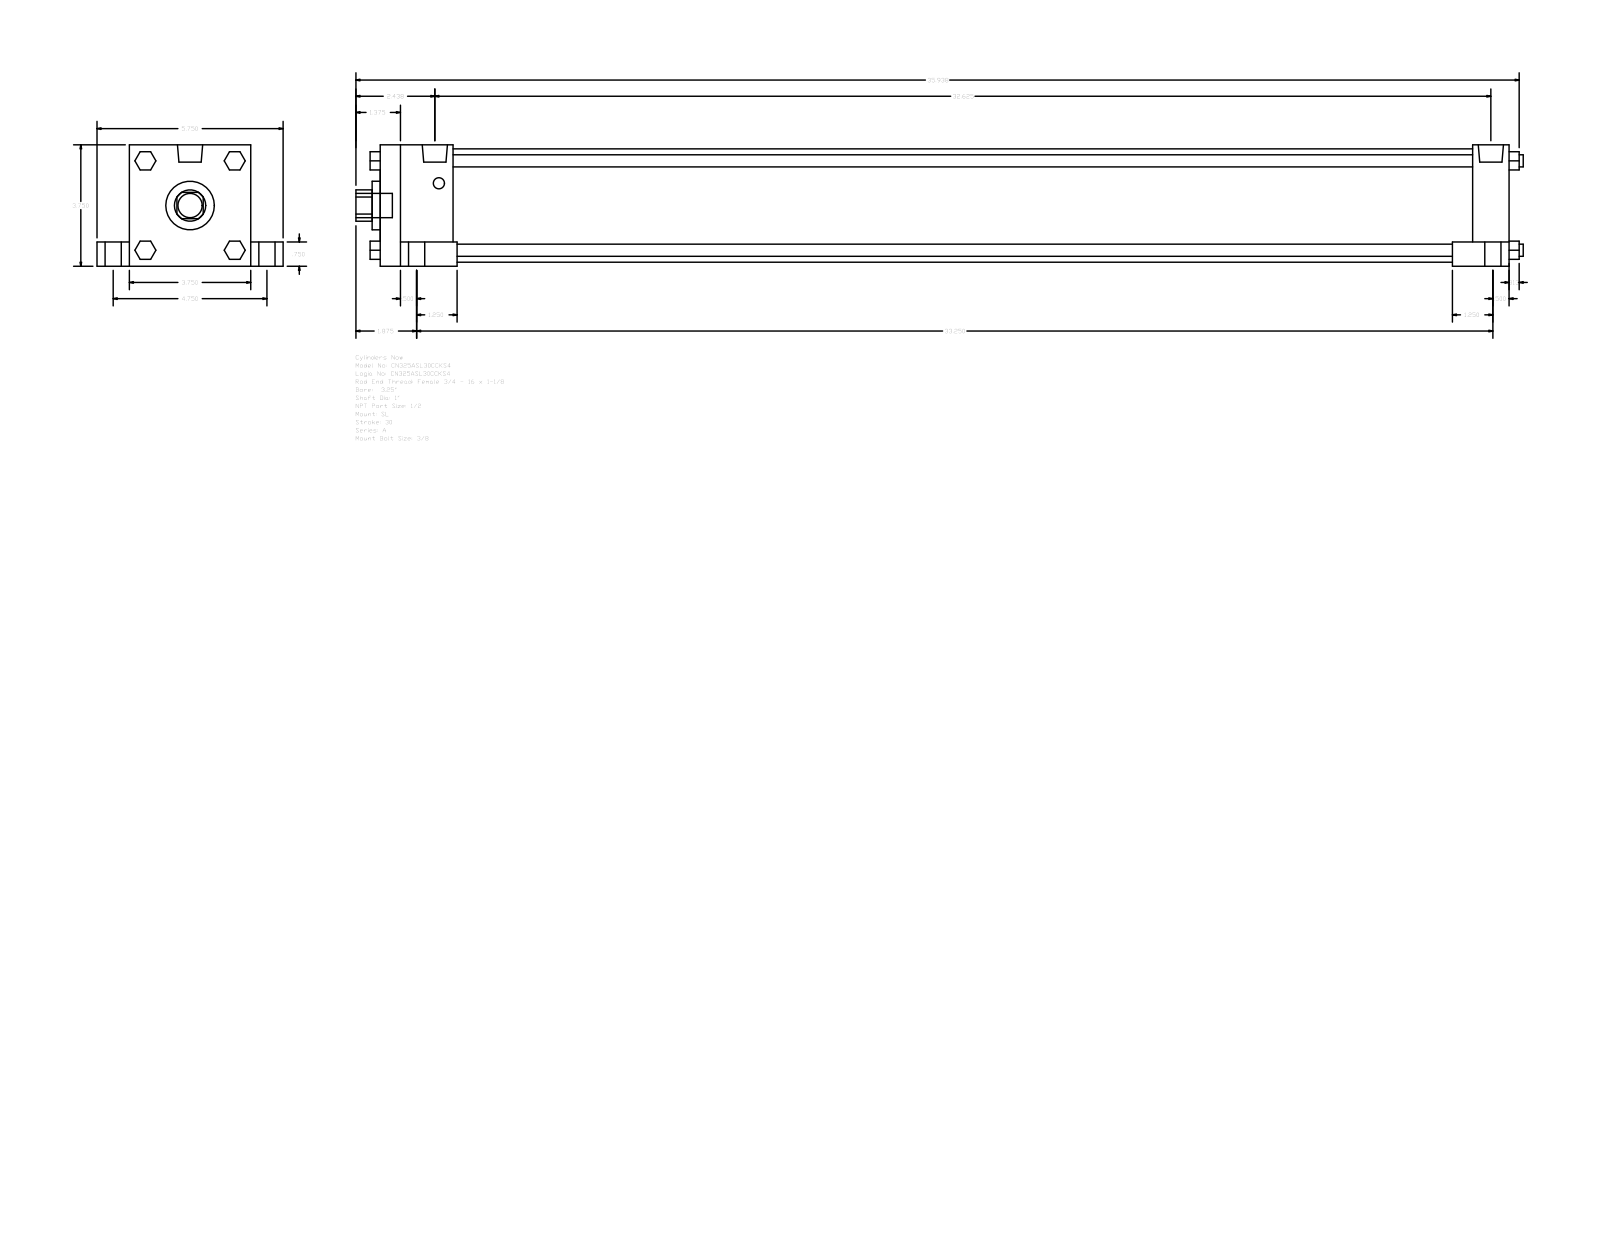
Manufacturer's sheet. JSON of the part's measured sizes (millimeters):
{"part_name": "A_SL__0325_1", "step_written_by": "GSSL Pune (CONFIG_CONTROL_DESIGN)", "units": "millimeters", "bodies": {"solids": 0, "faces": 150, "planar": 114, "cylindrical": 36, "other": 0}, "overall_size": [915.99, 146.05, 95.25], "round_holes": [[25.4, 1], [38.1, 1], [88.9, 1]], "round_bosses_or_shafts": [[19.05, 5], [12.7, 4], [9.53, 4], [8.73, 4], [19.77, 2]], "partial_cylinders_radius": [[12.29, 1]], "face_to_face_distances": [95.24, 885.83, 19.05, 25.41, 120.65, 76.19, 57.15, 857.25, 800.1, 828.68]}
